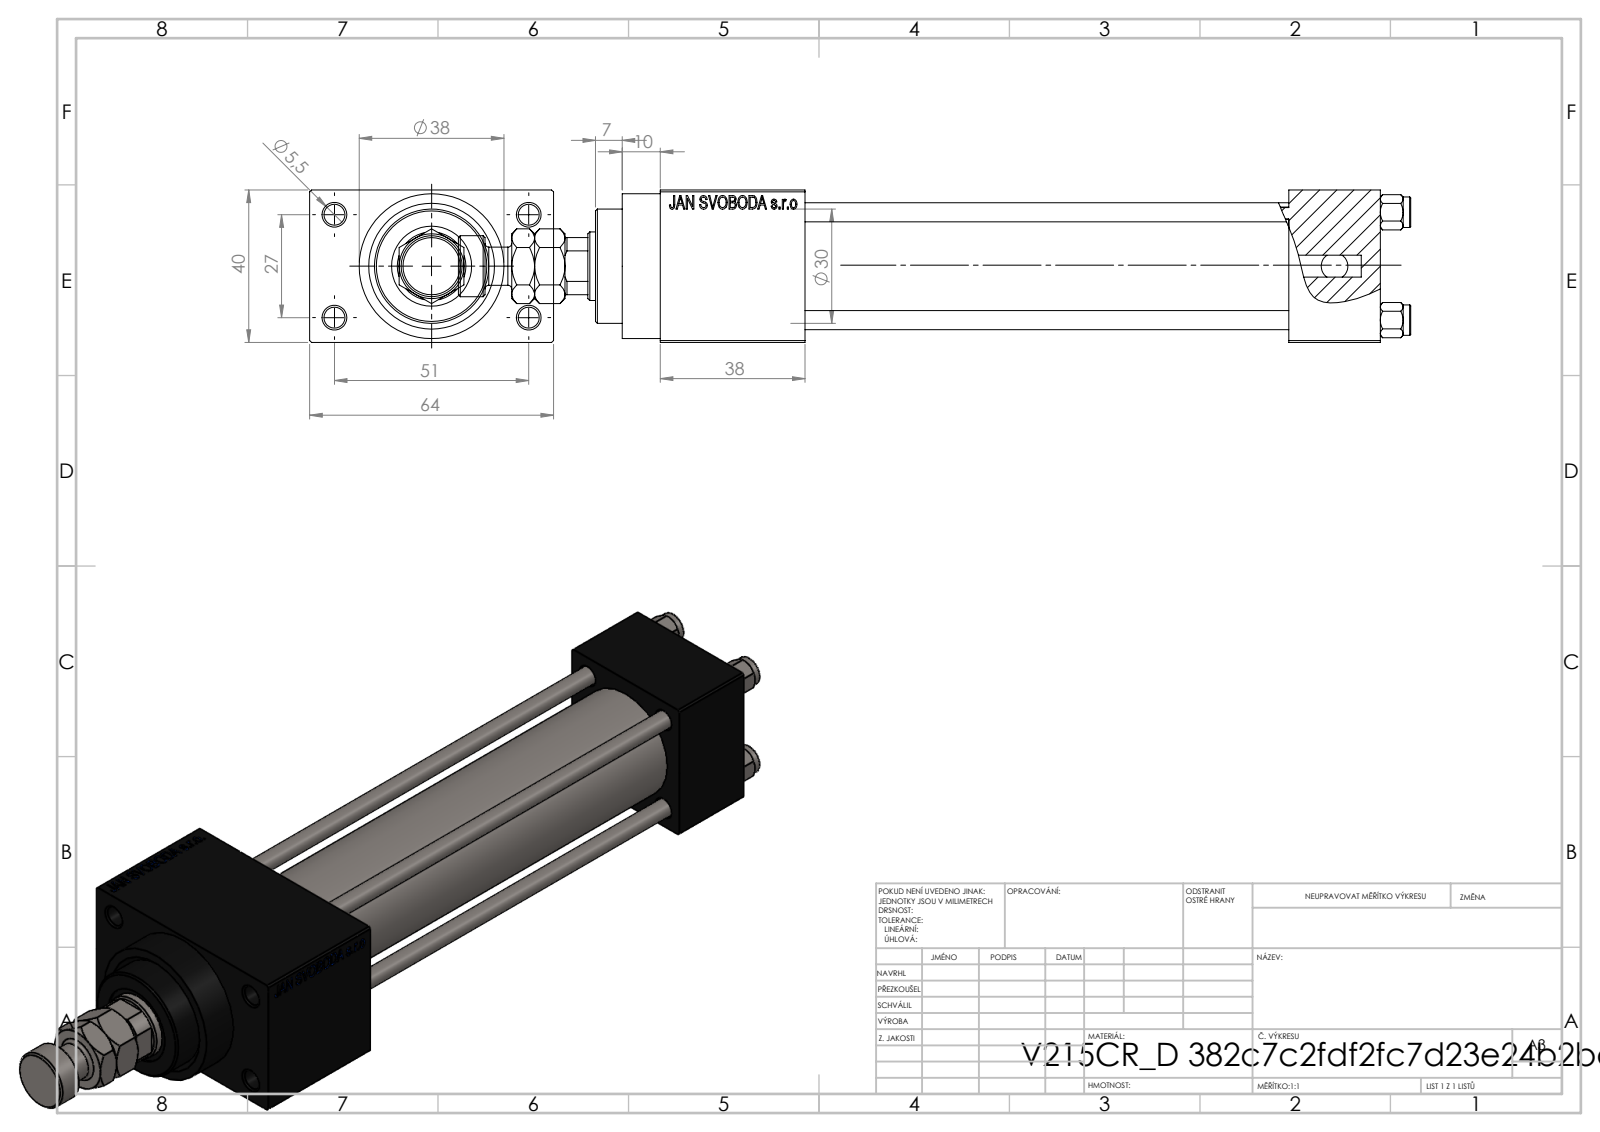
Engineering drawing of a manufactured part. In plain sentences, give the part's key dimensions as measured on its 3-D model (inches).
The part is named "V215CR_D_Body; NUT_M5_D; V215_VC_A; V215CR_VCP_D (+2 more)". Its 3-D file was written by "SolidWorks 2019 (CONFIG_CONTROL_DESIGN)". It is 12 solids with 1153 faces: 511 planar, 90 cylindrical and 552 other. Overall it measures 9.843 by 2.52 by 1.575 inches. Its volume is 14.18 cubic inches and its surface area 140 square inches. Round holes: 4 of diameter 0.197, 4 of diameter 0.217, 3 of diameter 0.787, 2 of diameter 0.276, 2 of diameter 0.518, 1 of diameter 0.335, 1 of diameter 0.709, 1 of diameter 0.827, 1 of diameter 0.984, 1 of diameter 1.181. Round bosses or shafts: 4 of diameter 0.315, 1 of diameter 1.496, 1 of diameter 1.22, 1 of diameter 0.63, 1 of diameter 0.394. Partial cylindrical surfaces (rounded edges, fillets, slot ends): 1 of radius 0.335. The main face-to-face distances are 1.575, 0.472, 5, 0.945, 5.945, 2.047, 1.496, 7.441, 6.496, 2.52. The hole center spacings are 0.448, 0.788, 1.114, 1.136, 1.177, 1.561, 1.903, 1.063.
